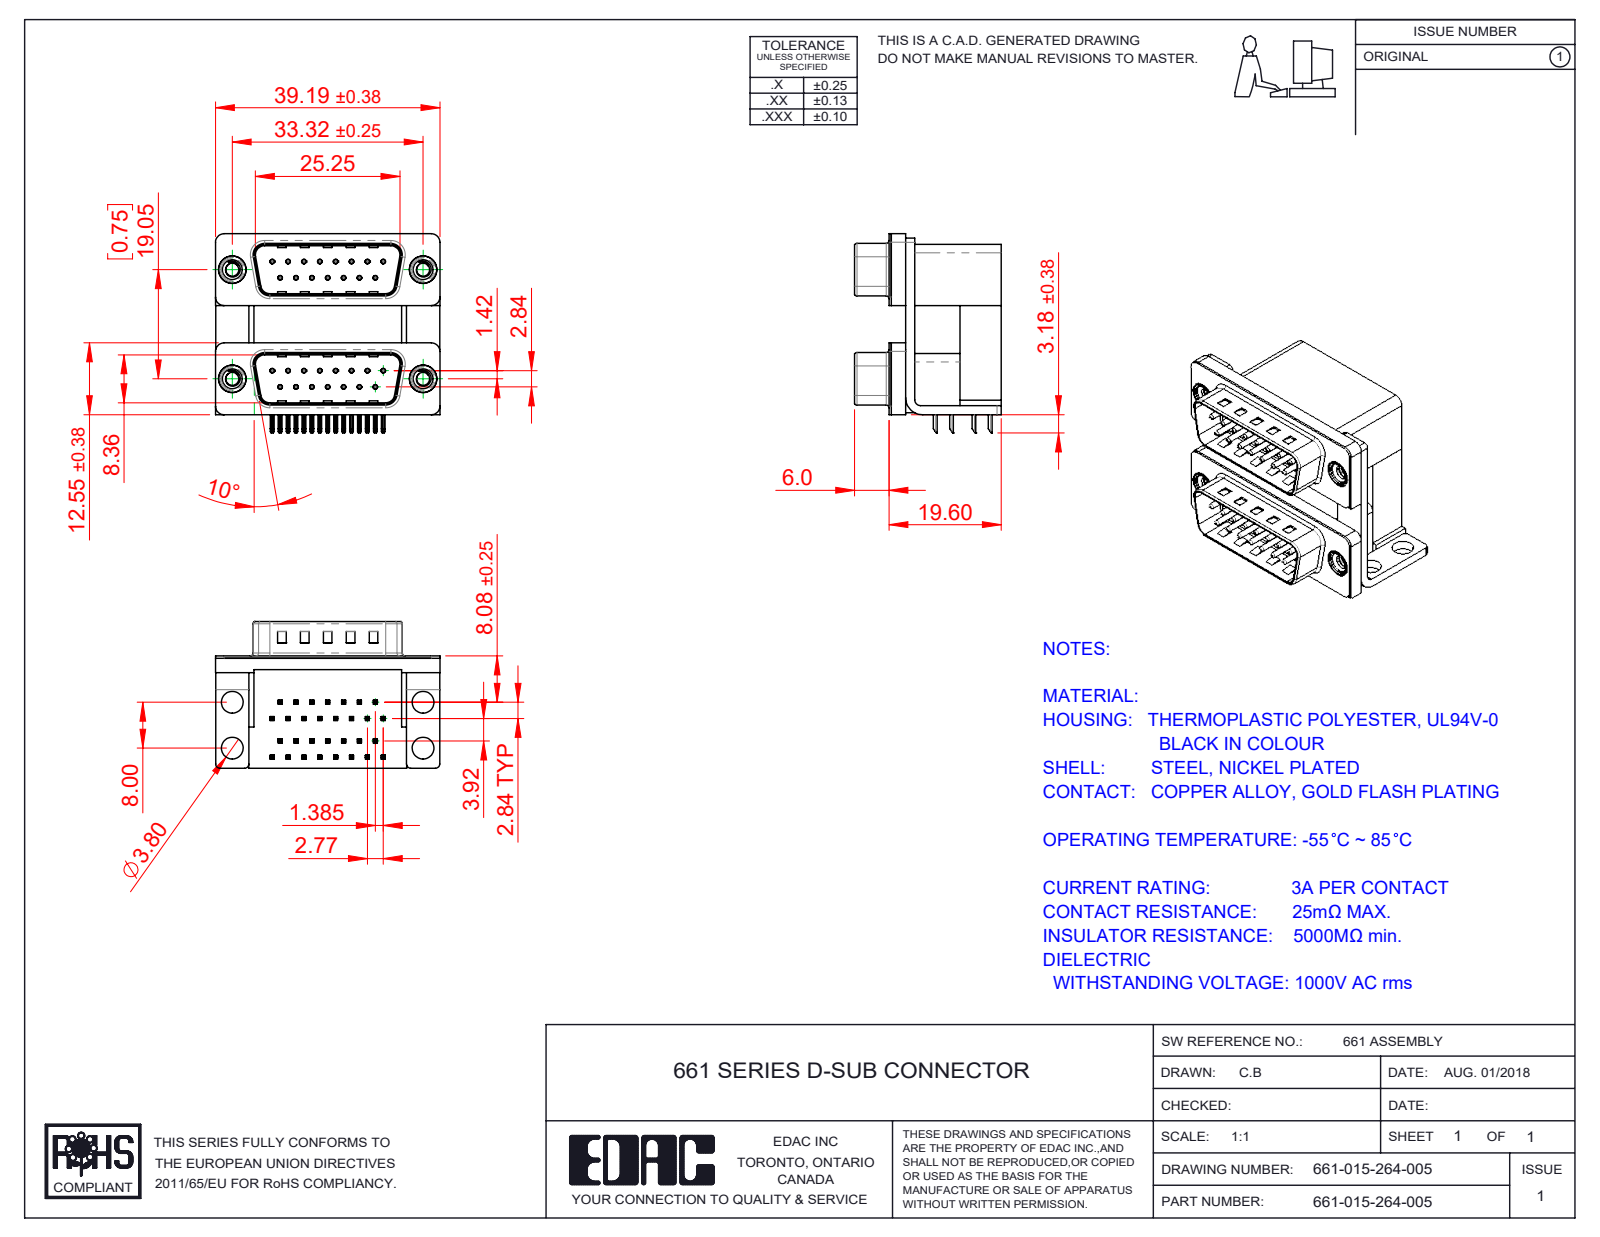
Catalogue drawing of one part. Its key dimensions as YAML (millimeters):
part_name: "661-015-264-005; 661 Housing Lower_15 Contacts; 661 Contact Top Lower; 661 Contact Top Upper_M (+7 more)"
step_written_by: "SolidWorks 2020 (CONFIG_CONTROL_DESIGN)"
units: millimeters
bodies: {solids: 41, faces: 2962, planar: 1834, cylindrical: 854, other: 274}
overall_size: [39.19, 34.78, 25.6]
volume: 14374
surface_area: 15615
round_holes:
  - {diameter: 0.35, count: 30}
  - {diameter: 0.8, count: 30}
  - {diameter: 2.26, count: 4}
  - {diameter: 3.5, count: 4}
  - {diameter: 3.8, count: 4}
  - {diameter: 4, count: 4}
  - {diameter: 4.8, count: 4}
  - {diameter: 5, count: 4}
round_bosses_or_shafts:
  - {diameter: 0.75, count: 30}
  - {diameter: 4.9, count: 4}
  - {diameter: 4.75, count: 4}
  - {diameter: 3.9, count: 4}
partial_cylinders:
  - {radius: 0.25, count: 120}
  - {radius: 0.12, count: 60}
  - {radius: 0.5, count: 16}
  - {radius: 1.5, count: 16}
  - {radius: 0.75, count: 8}
  - {radius: 0.9, count: 8}
  - {radius: 1.6, count: 8}
  - {radius: 2, count: 8}
face_to_face_distances: [0.4, 19.05, 19.2, 10.69, 16.7, 2.5, 7.2, 12, 9.5, 18.7]
hole_center_spacings: [3.16, 2.77, 19.25, 5.54, 19.84, 8.31, 20.78, 19.05]
